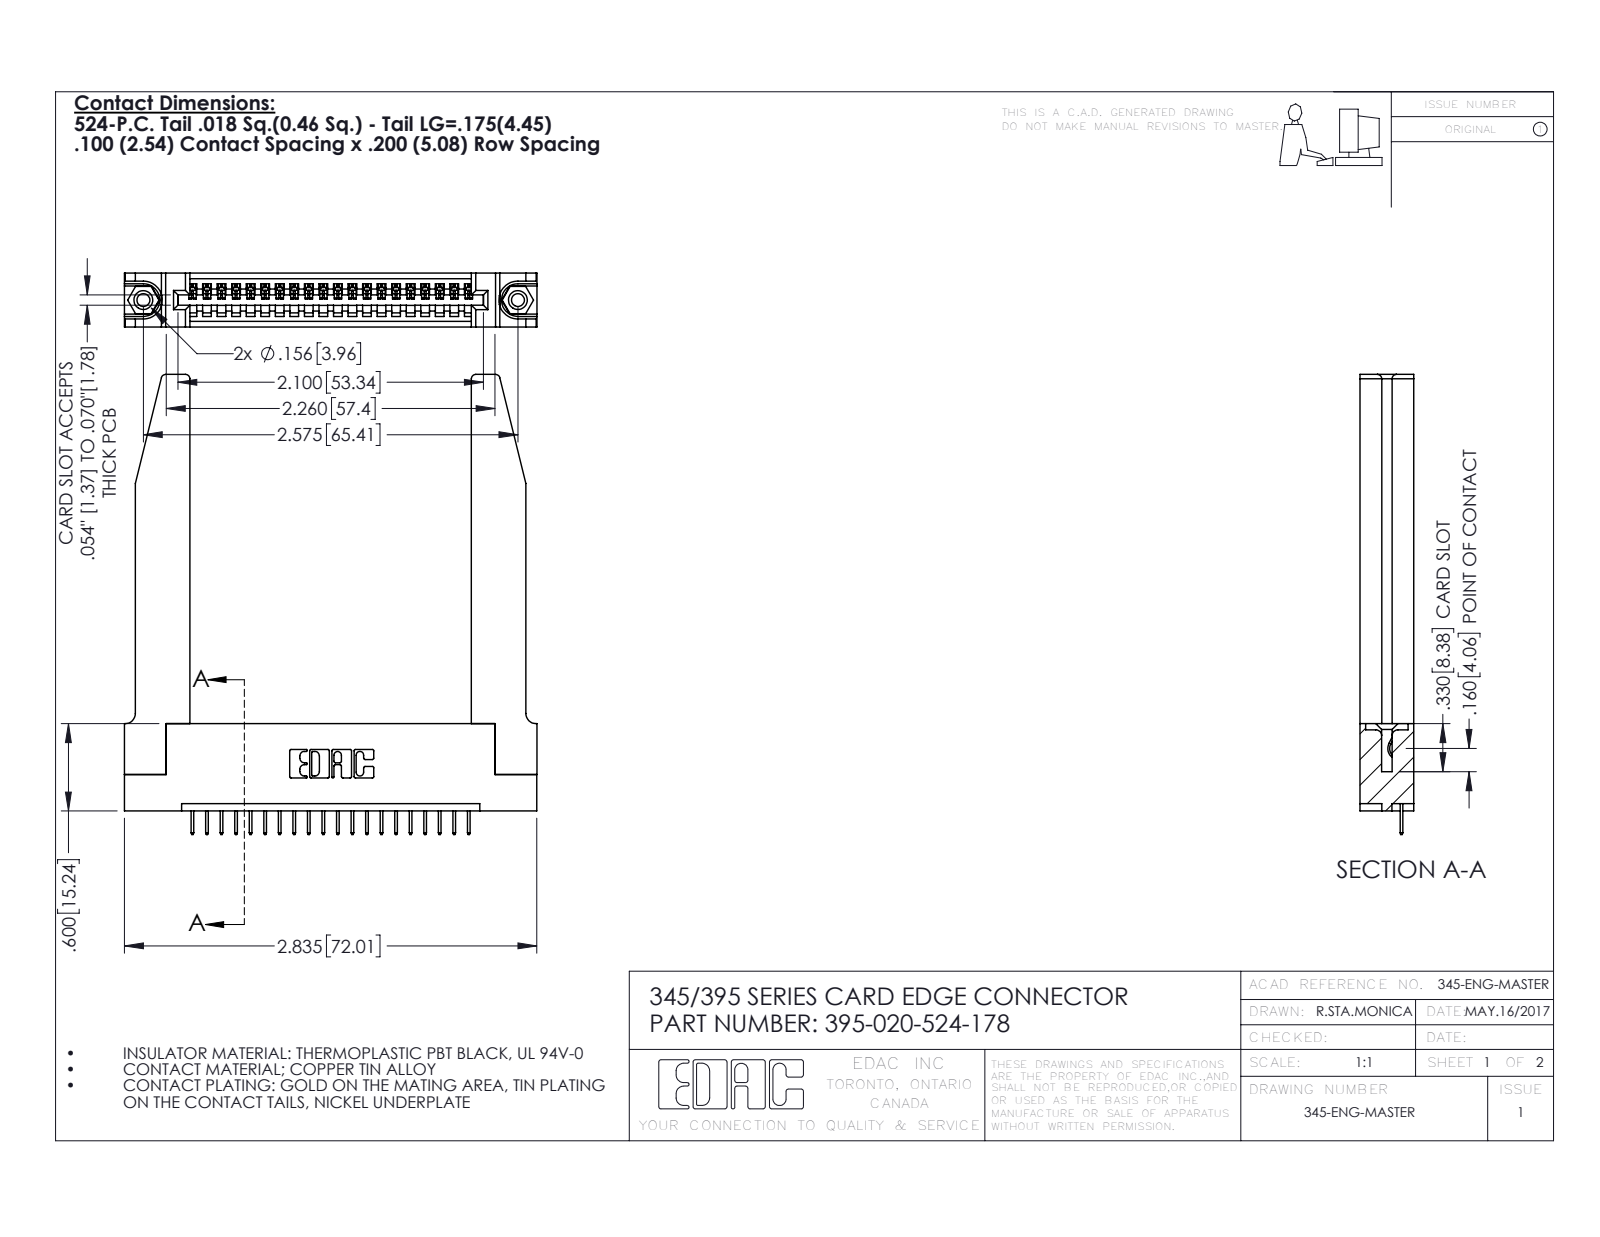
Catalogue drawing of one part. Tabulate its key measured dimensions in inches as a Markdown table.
| quantity | value |
| --- | --- |
| part name | 345-250-001_345-250-001-102; 345-220-078_345-220-078; 395-020-524-178; 345-292-001_345-293-124 (+1 more) |
| STEP written by | SolidWorks 2016 (CONFIG_CONTROL_DESIGN) |
| units | inches |
| bodies | 25 solids, 1600 faces (1142 planar, 406 cylindrical, 52 other) |
| overall size | 3.162 × 2.836 × 0.37 |
| volume | 0.876 in³ |
| surface area | 23.31 in² |
| round holes (diameter × count) | 0.089 × 2, 0.125 × 2, 0.156 × 2, 0.064 × 1 |
| round bosses / shafts (diameter × count) | 0.155 × 2 |
| partial cylindrical surfaces (radius × count) | 0.006 × 40, 0.01 × 22, 0.03 × 8, 0.007 × 6, 0.031 × 6, 0.026 × 3, 0.031 × 2, 0.04 × 2 |
| main face-to-face distances | 0.37, 0.072, 0.298, 0.2, 0.148, 0.15, 0.098, 0.272, 0.025, 0.077 |
| hole center spacings | 0.27, 2.341, 2.575 |
